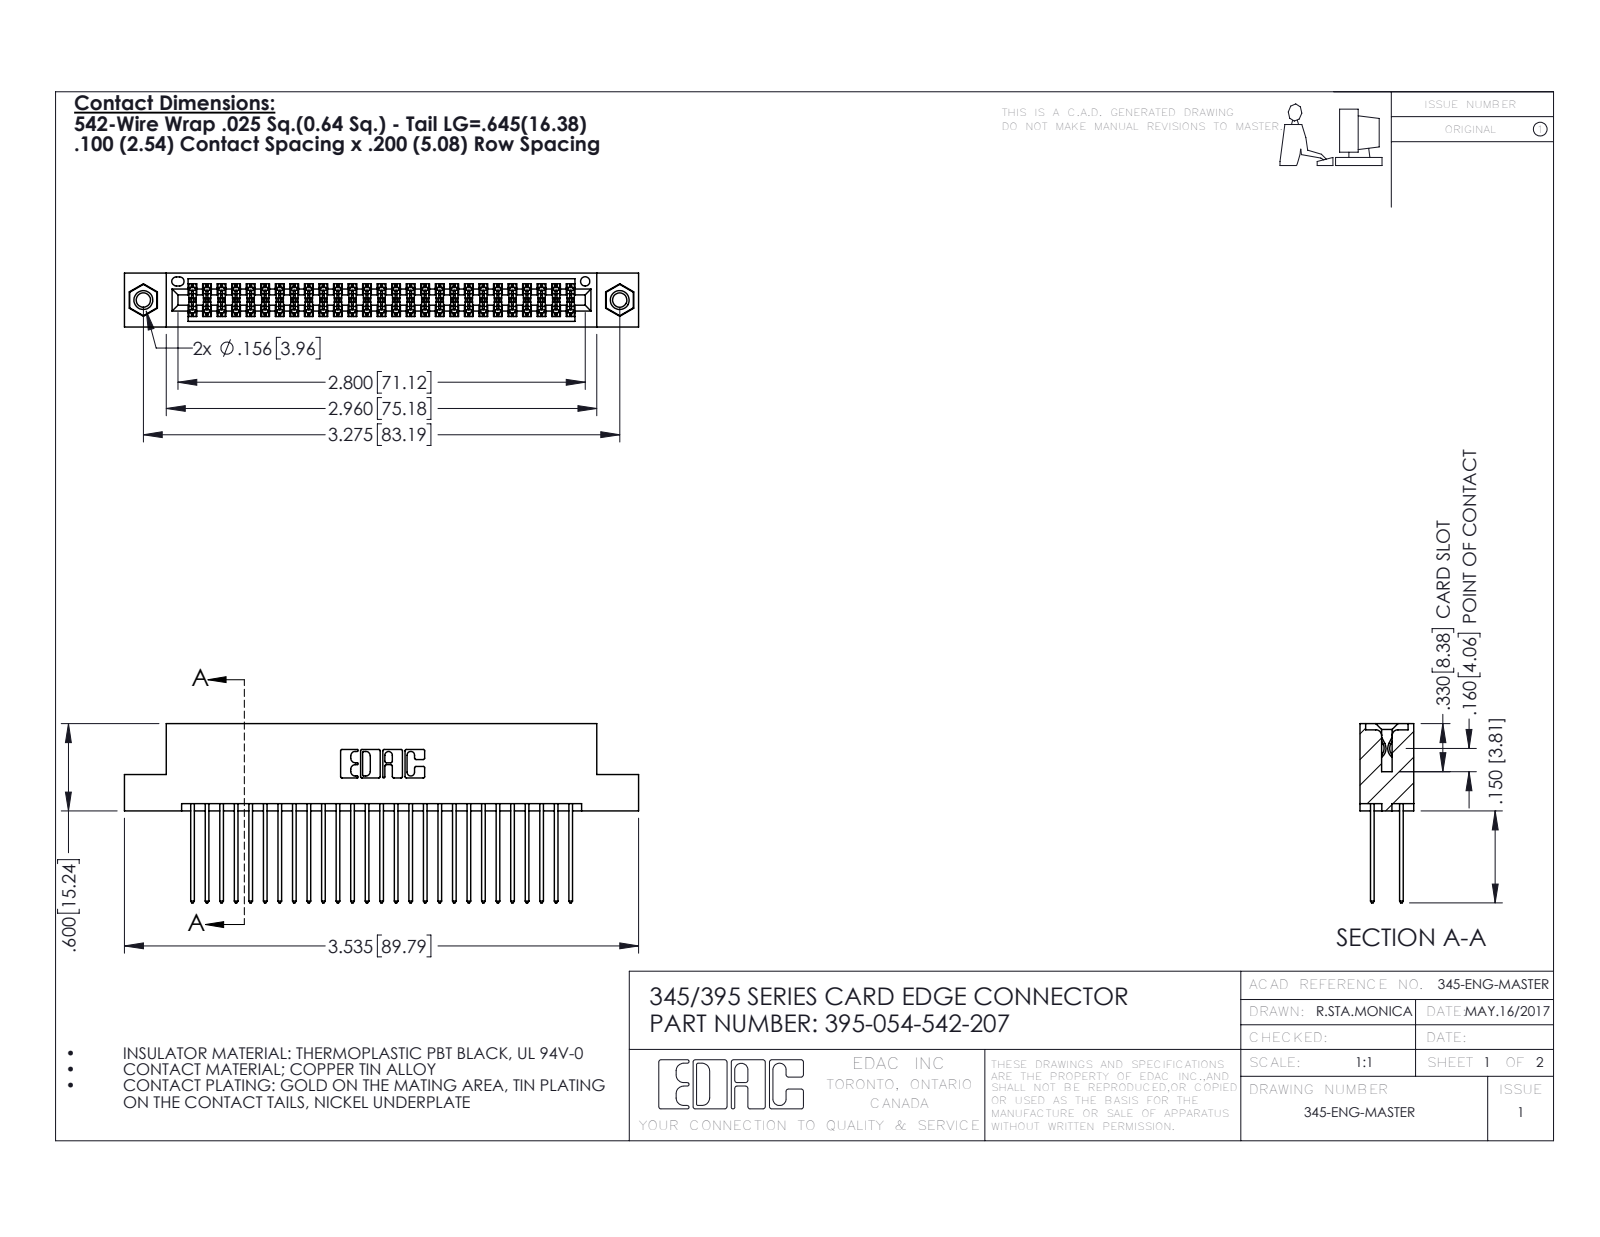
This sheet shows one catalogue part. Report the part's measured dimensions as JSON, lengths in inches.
{"part_name": "395-054-542-207; 345-250-001_345-250-005-103; 345 Part_Flush Mounting Lugs - 0.156 Dia-TI; 345-292-001_345-293-142", "step_written_by": "SolidWorks 2016 (CONFIG_CONTROL_DESIGN)", "units": "inches", "bodies": {"solids": 57, "faces": 2886, "planar": 1894, "cylindrical": 976, "other": 16}, "overall_size": [3.535, 1.232, 0.37], "volume_in3": 0.538, "surface_area_in2": 21.63, "round_holes": [[0.098, 2], [0.125, 2], [0.156, 2], [0.064, 1]], "round_bosses_or_shafts": [[0.155, 2]], "partial_cylinders_radius": [[0.006, 81], [0.01, 54], [0.01, 22], [0.007, 6], [0.031, 6], [0.026, 3], [0.014, 2], [0.019, 2]], "face_to_face_distances": [0.072, 0.298, 0.2, 0.098, 0.272, 0.025, 0.37, 0.225, 0.175, 0.149], "hole_center_spacings": [0.27, 3.04, 3.275]}
